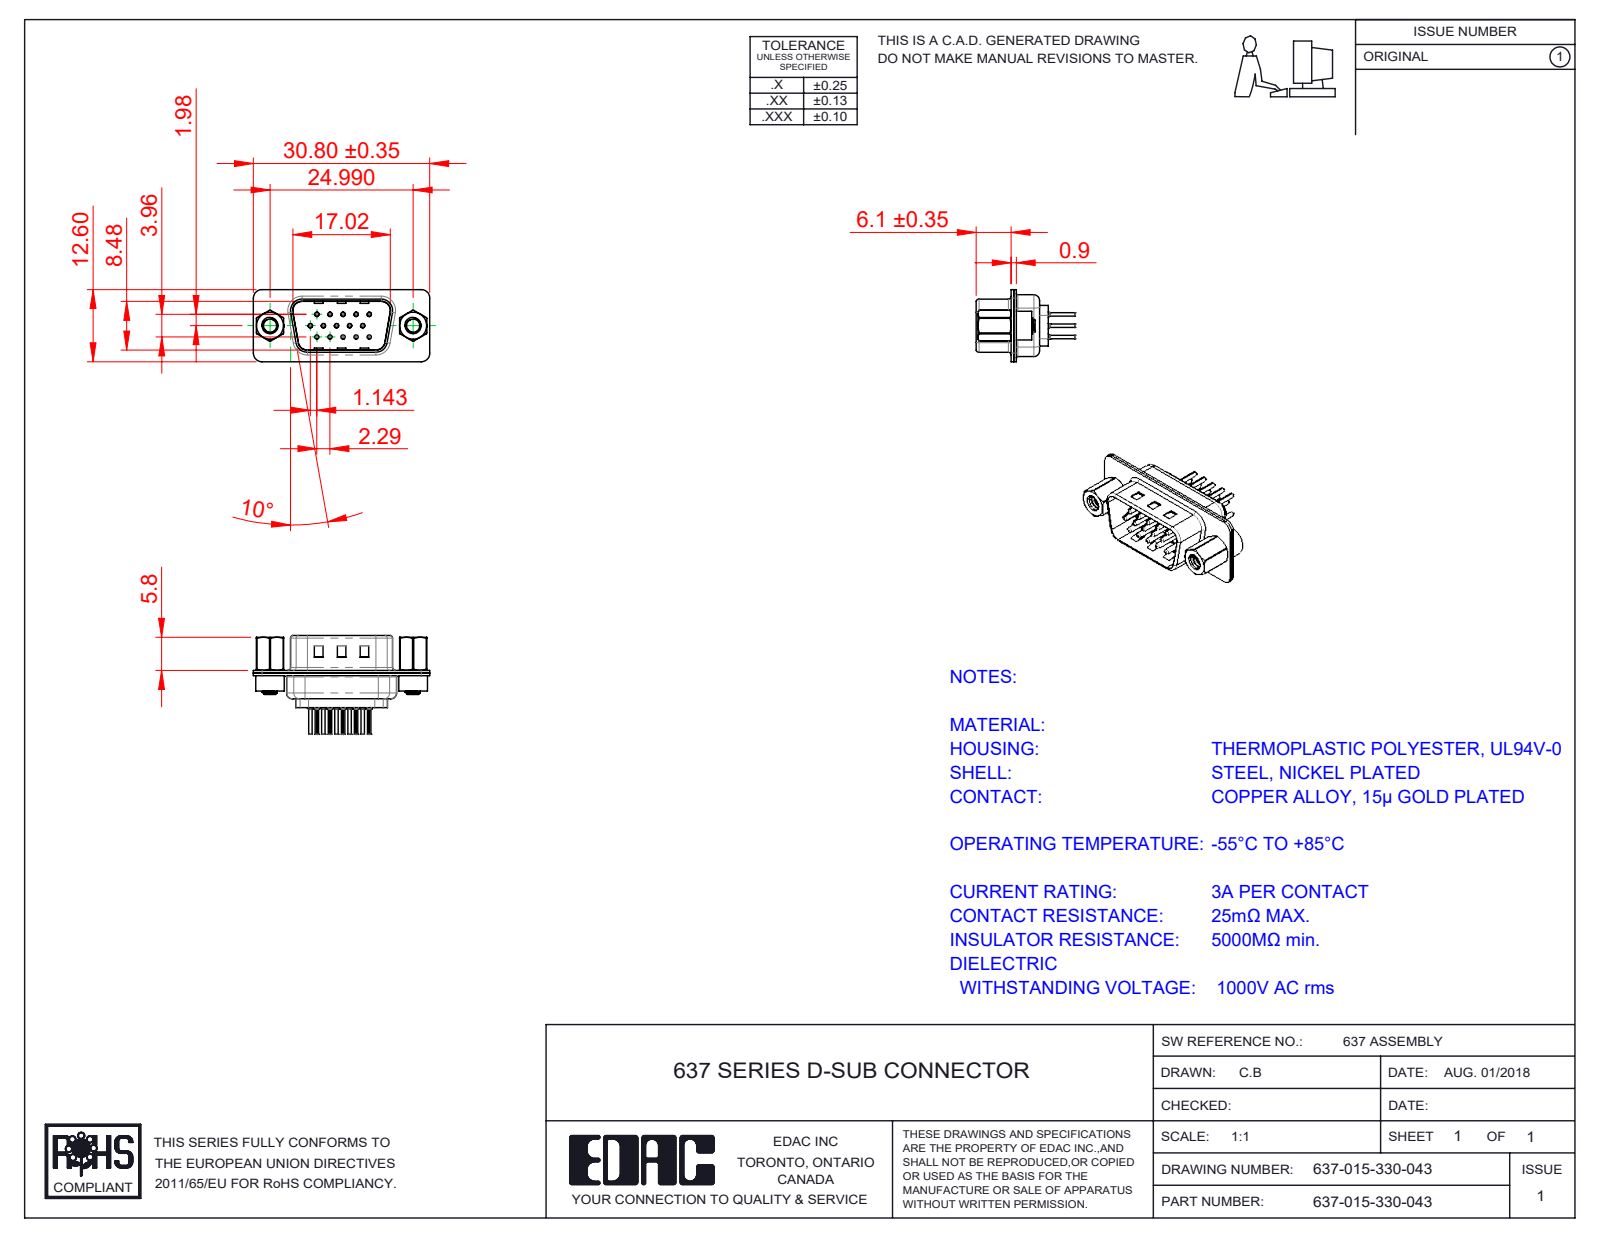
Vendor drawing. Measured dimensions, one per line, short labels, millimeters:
name: 637 Contact Row 2_30; 637 Housing_15 Contacts; 637 Shell Front_15 Contacts; 637 Contact Row 1_30 (+5 more)
written by: SolidWorks 2020 (CONFIG_CONTROL_DESIGN)
unit: mm
bodies: 22 solids, 1930 faces (489 planar, 756 cylindrical, 685 other)
size: 30.8 × 17.25 × 12.6
volume: 1 529 mm³; area: 5 130 mm²
holes: 15× ⌀0.2, 15× ⌀0.35, 15× ⌀1.1, 15× ⌀1.6, 2× ⌀2.26, 2× ⌀2.29, 2× ⌀4, 2× ⌀4.8
bosses: 15× ⌀2, 15× ⌀1.5, 15× ⌀0.75, 15× ⌀0.6, 2× ⌀5, 2× ⌀4.9, 2× ⌀2.79
rounds: 30× R0.1, 16× R1.5, 12× R2, 8× R0.5, 4× R0.25, 4× R0.55, 4× R0.7, 4× R0.95
face distances: 0.45, 0.9, 0.4, 0.7, 8.88, 8.48, 1.05, 0.31, 4.55, 6.5
hole spacings: 3.96, 2.28, 4.57, 2.29, 6.05, 6.86, 7.92, 6.04
